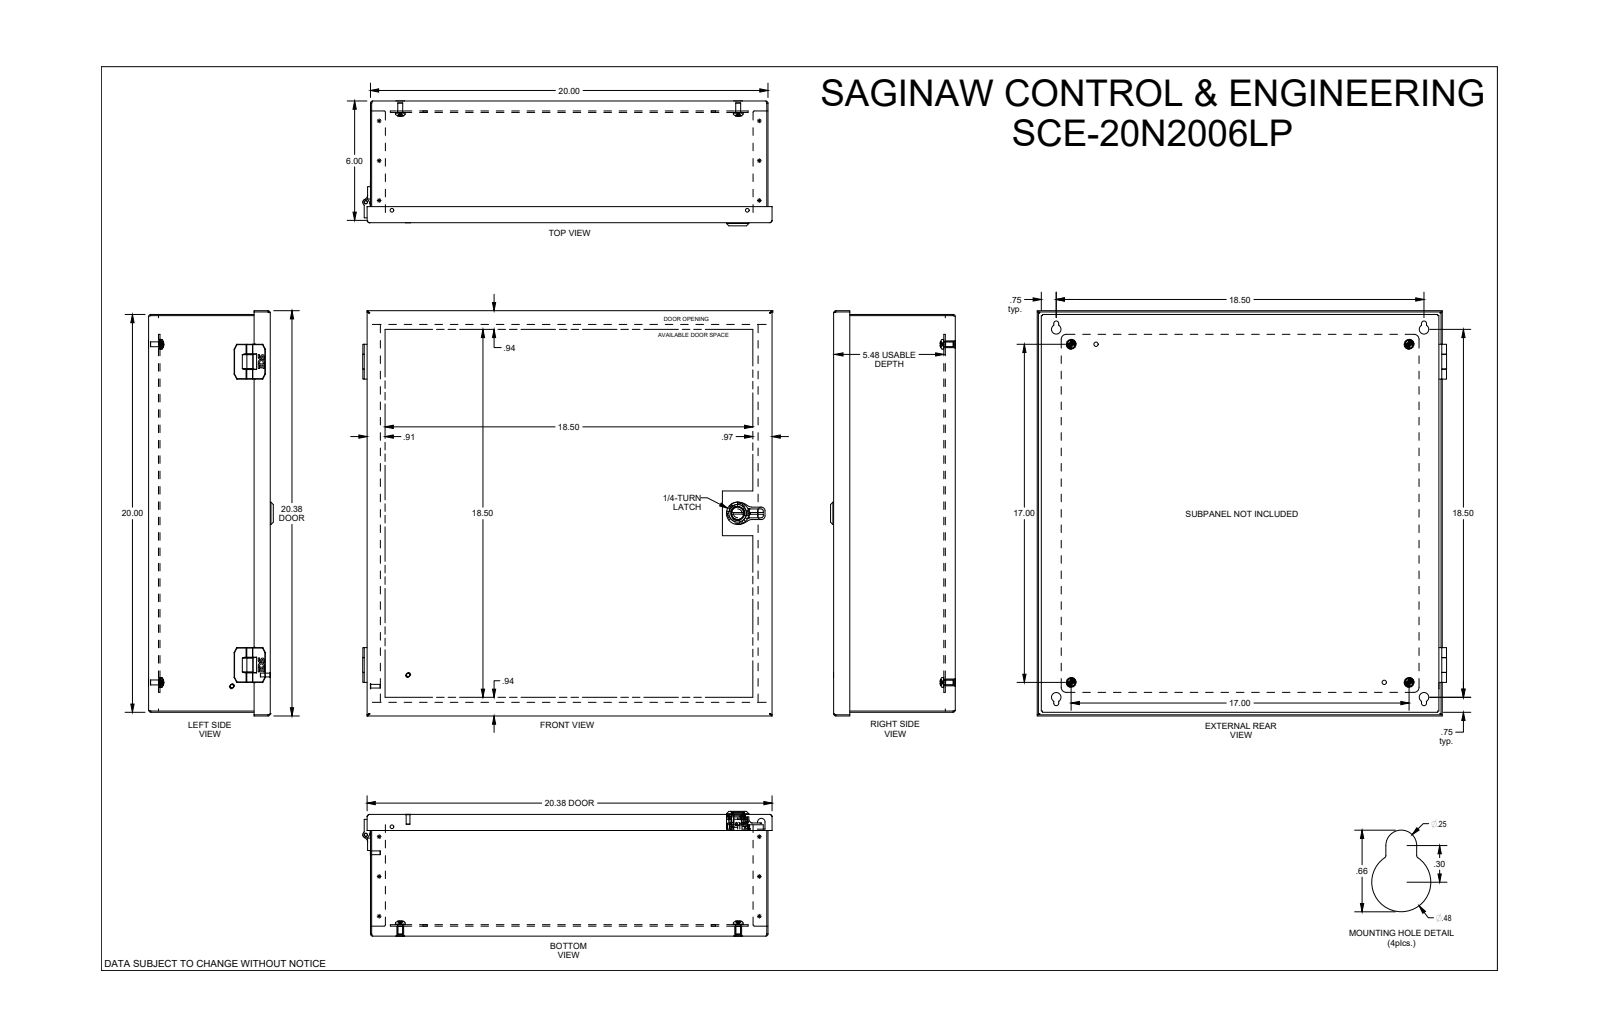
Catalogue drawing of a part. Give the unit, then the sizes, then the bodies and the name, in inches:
Units: inches
Overall size (bounding box): 20.593 × 20.375 × 6.279
Round holes (diameter × count): ⌀0.25 ×4, ⌀0.281 ×4, ⌀0.329 ×4, ⌀0.343 ×4, ⌀0.479 ×4, ⌀0.48 ×4, ⌀0.187 ×2, ⌀0.193 ×2, ⌀0.218 ×2, ⌀0.158 ×1, ⌀0.44 ×1, ⌀0.635 ×1
Round bosses / shafts (diameter × count): ⌀0.492 ×4, ⌀0.341 ×4, ⌀0.248 ×4, ⌀0.237 ×4, ⌀0.17 ×4, ⌀0.16 ×4, ⌀0.135 ×4, ⌀0.108 ×4
Partial cylindrical surfaces — rounded edges, fillets, slot ends (radius × count): R0.01 ×253, R0.106 ×132, R0.005 ×130, R0.02 ×103, R0.015 ×32, R0.025 ×24, R0.052 ×16, R0.112 ×16
Main face-to-face distances: 0.06, 6.059, 19.94, 6.119, 5.999, 0.5, 0.44, 0.575, 0.515, 5.484
Hole centre spacings: 17.766, 1.061, 17, 18.5, 25.102, 1.091, 1.25, 2.136
Bodies: 0 solids, 3058 faces (1038 planar, 1032 cylindrical, 988 other)
Part name (STEP PRODUCT): SCE-20N2006LP
STEP written by: SolidWorks 2019 (CONFIG_CONTROL_DESIGN)
